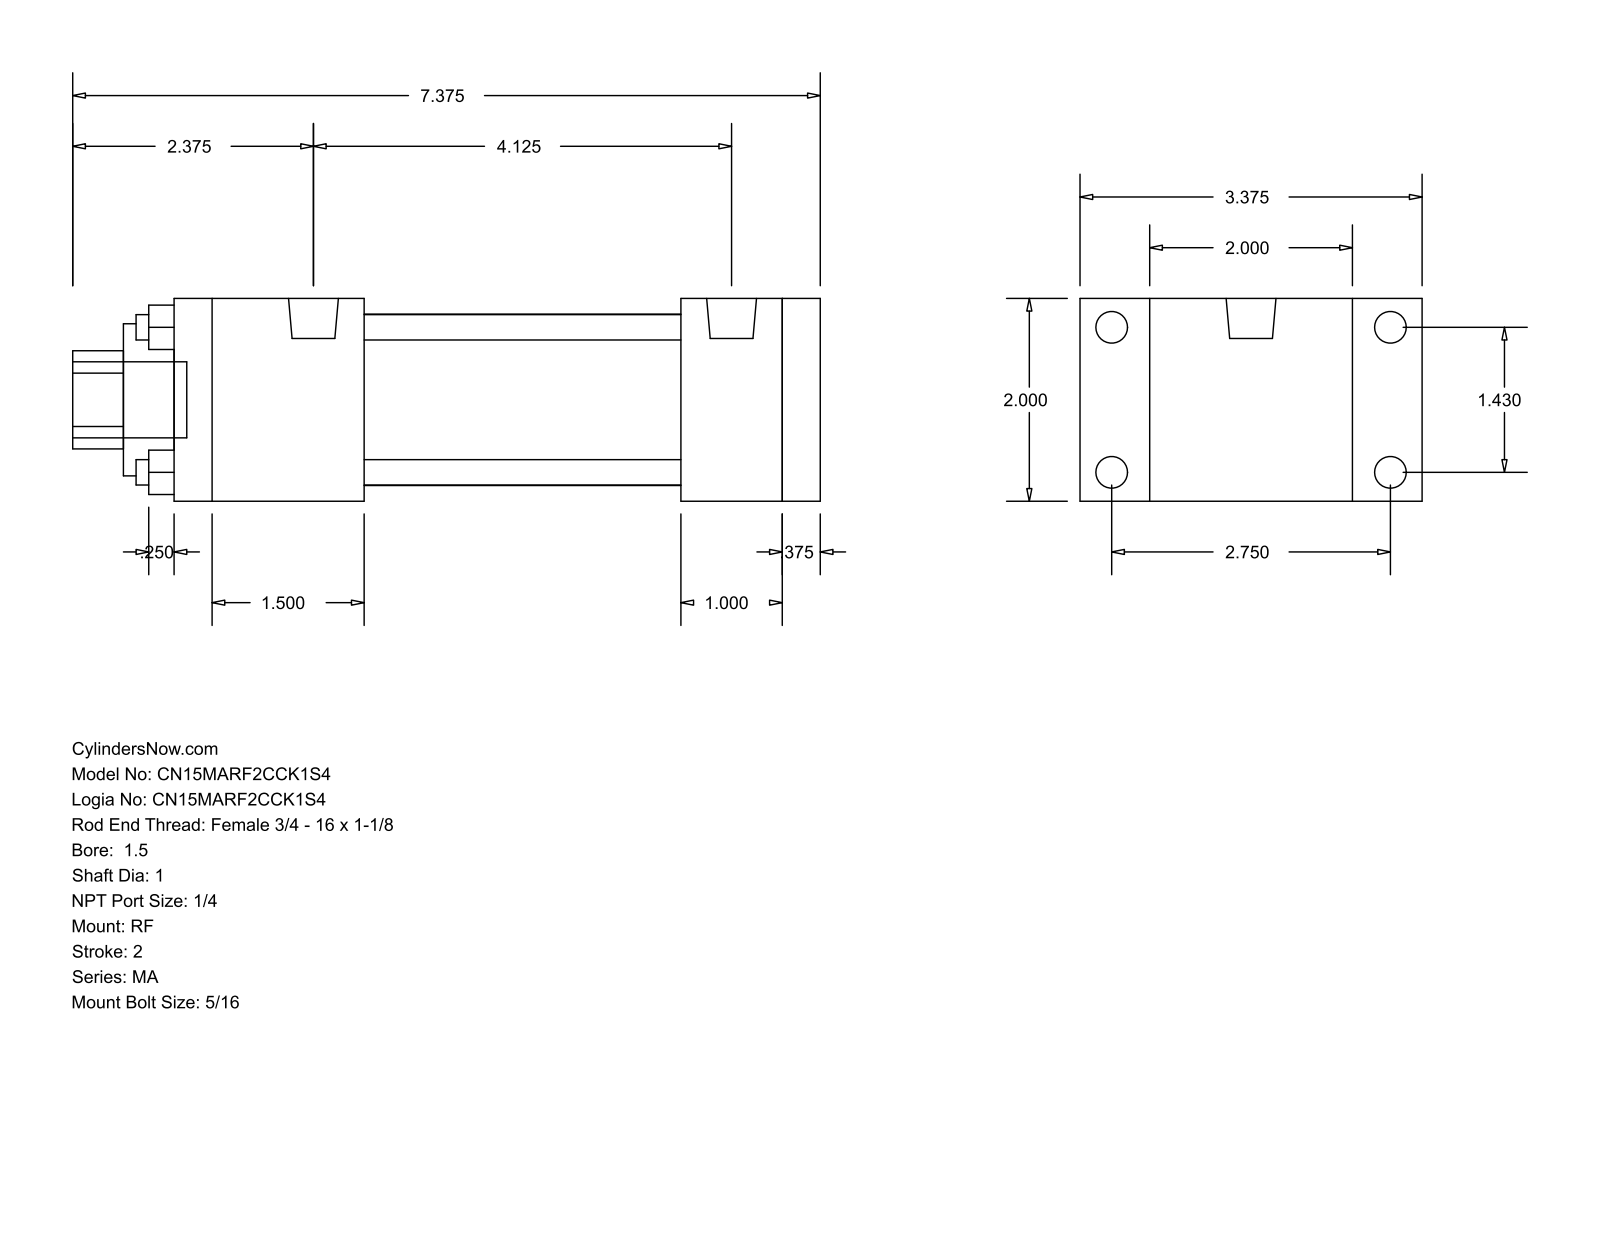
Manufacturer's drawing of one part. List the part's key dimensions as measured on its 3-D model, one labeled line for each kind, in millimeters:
Part name (STEP PRODUCT): MA_RF__0150_1
STEP written by: GSSL Pune (CONFIG_CONTROL_DESIGN)
Units: millimetres
Bodies: 0 solids, 92 faces (64 planar, 28 cylindrical, 0 other)
Overall size (bounding box): 187.32 × 85.72 × 50.8
Round holes (diameter × count): ⌀6.35 ×4, ⌀25.4 ×1, ⌀38.1 ×1, ⌀42.93 ×1
Round bosses / shafts (diameter × count): ⌀7.94 ×8, ⌀12.49 ×2, ⌀19.05 ×1
Partial cylindrical surfaces — rounded edges, fillets, slot ends (radius × count): R12.29 ×1
Main face-to-face distances: 50.8, 9.52, 161.92, 152.4, 25.4, 127, 34.92, 47.63, 79.37, 104.77
Hole centre spacings: 25.68, 36.32, 51.36
